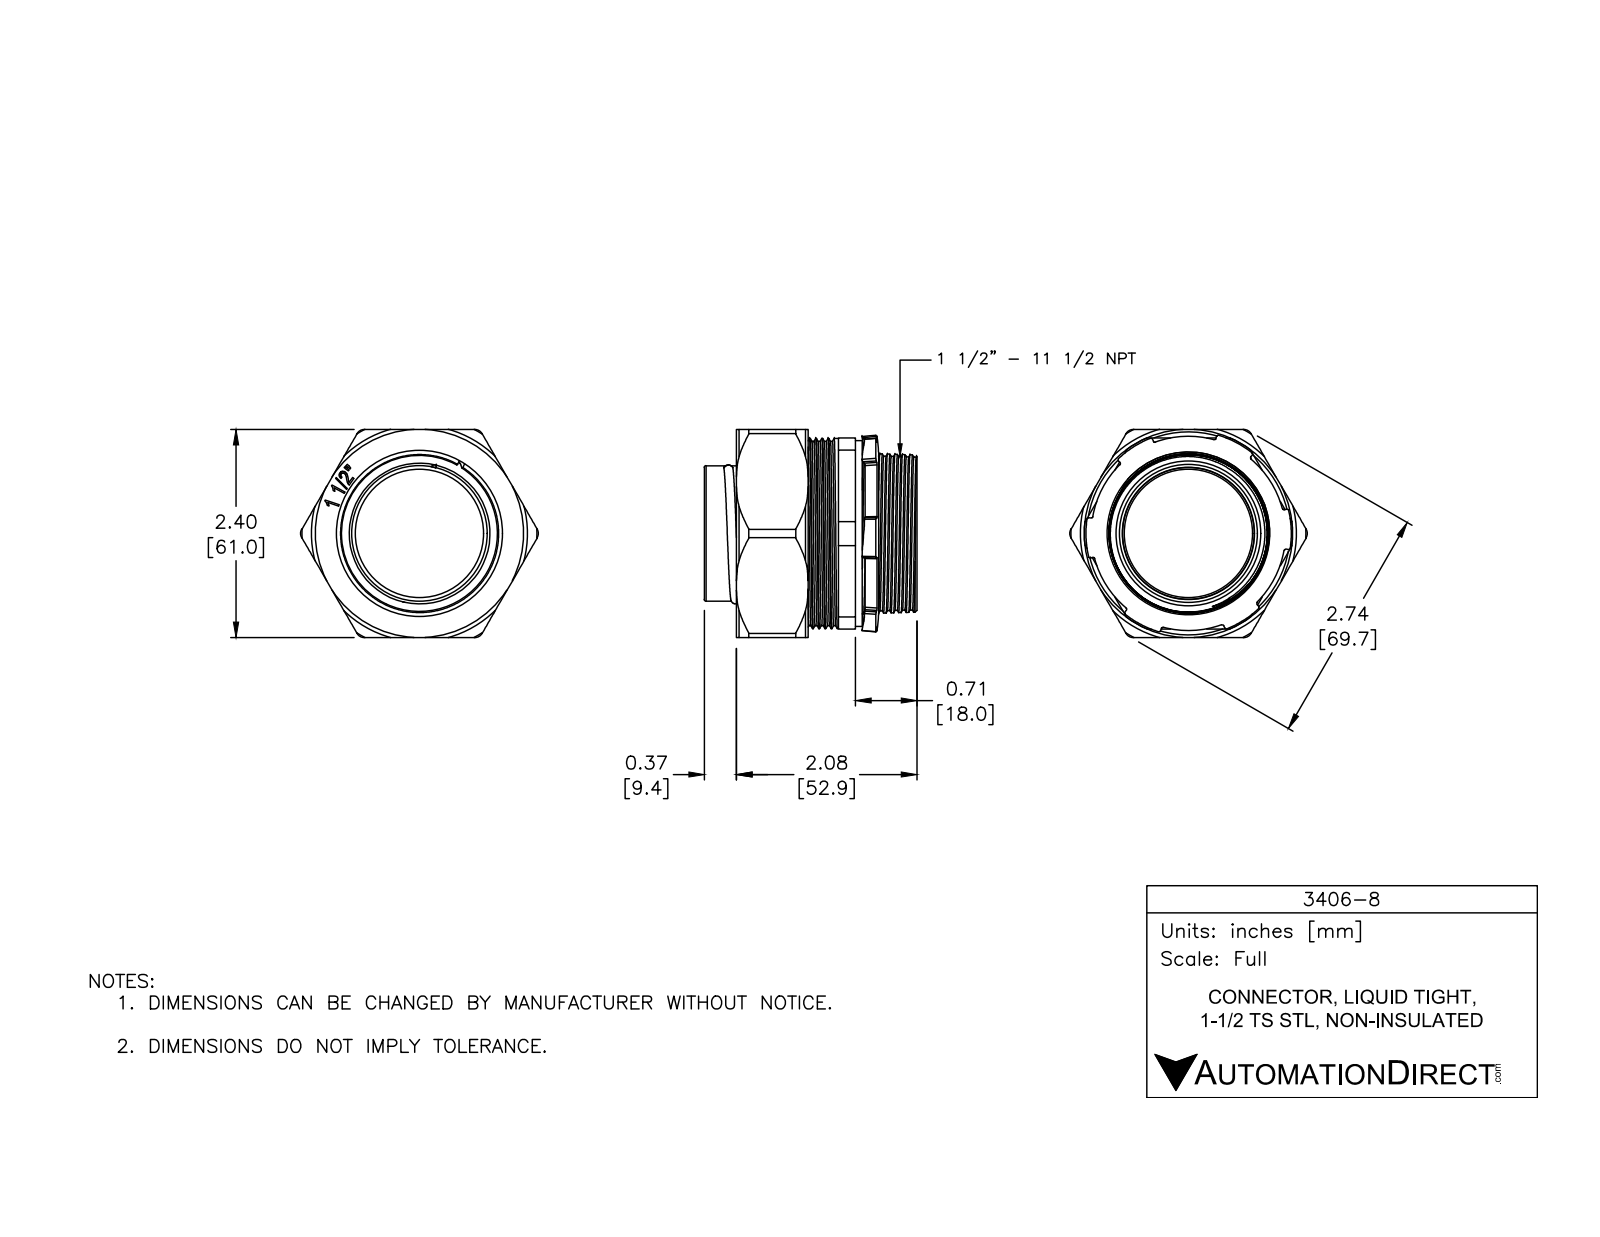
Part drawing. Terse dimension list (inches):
name: 3406-8
written by: SolidWorks 2018 (AUTOMOTIVE_DESIGN)
unit: in
bodies: 6 solids, 538 faces (212 planar, 117 cylindrical, 209 other)
size: 2.744 × 2.453 × 2.402
volume: 2.981 in³; area: 81.3 in²
holes: 1× ⌀0.192, 1× ⌀1.482, 1× ⌀1.524, 1× ⌀1.591, 1× ⌀1.795, 1× ⌀1.878, 1× ⌀1.917, 1× ⌀1.93, 1× ⌀1.996, 1× ⌀2.165
bosses: 1× ⌀2.196, 1× ⌀2.146, 1× ⌀2.098, 1× ⌀1.969, 1× ⌀1.563, 1× ⌀1.522, 1× ⌀0.156
rounds: 8× R0.012, 6× R0.094, 2× R0.004, 2× R0.052, 1× R0.006, 1× R0.016, 1× R0.024, 1× R1.201
face distances: 2.402, 1.374, 2.304, 2.402, 1.138, 0.236, 0.079, 1.453, 0.315, 0.098
hole spacings: 1.085
